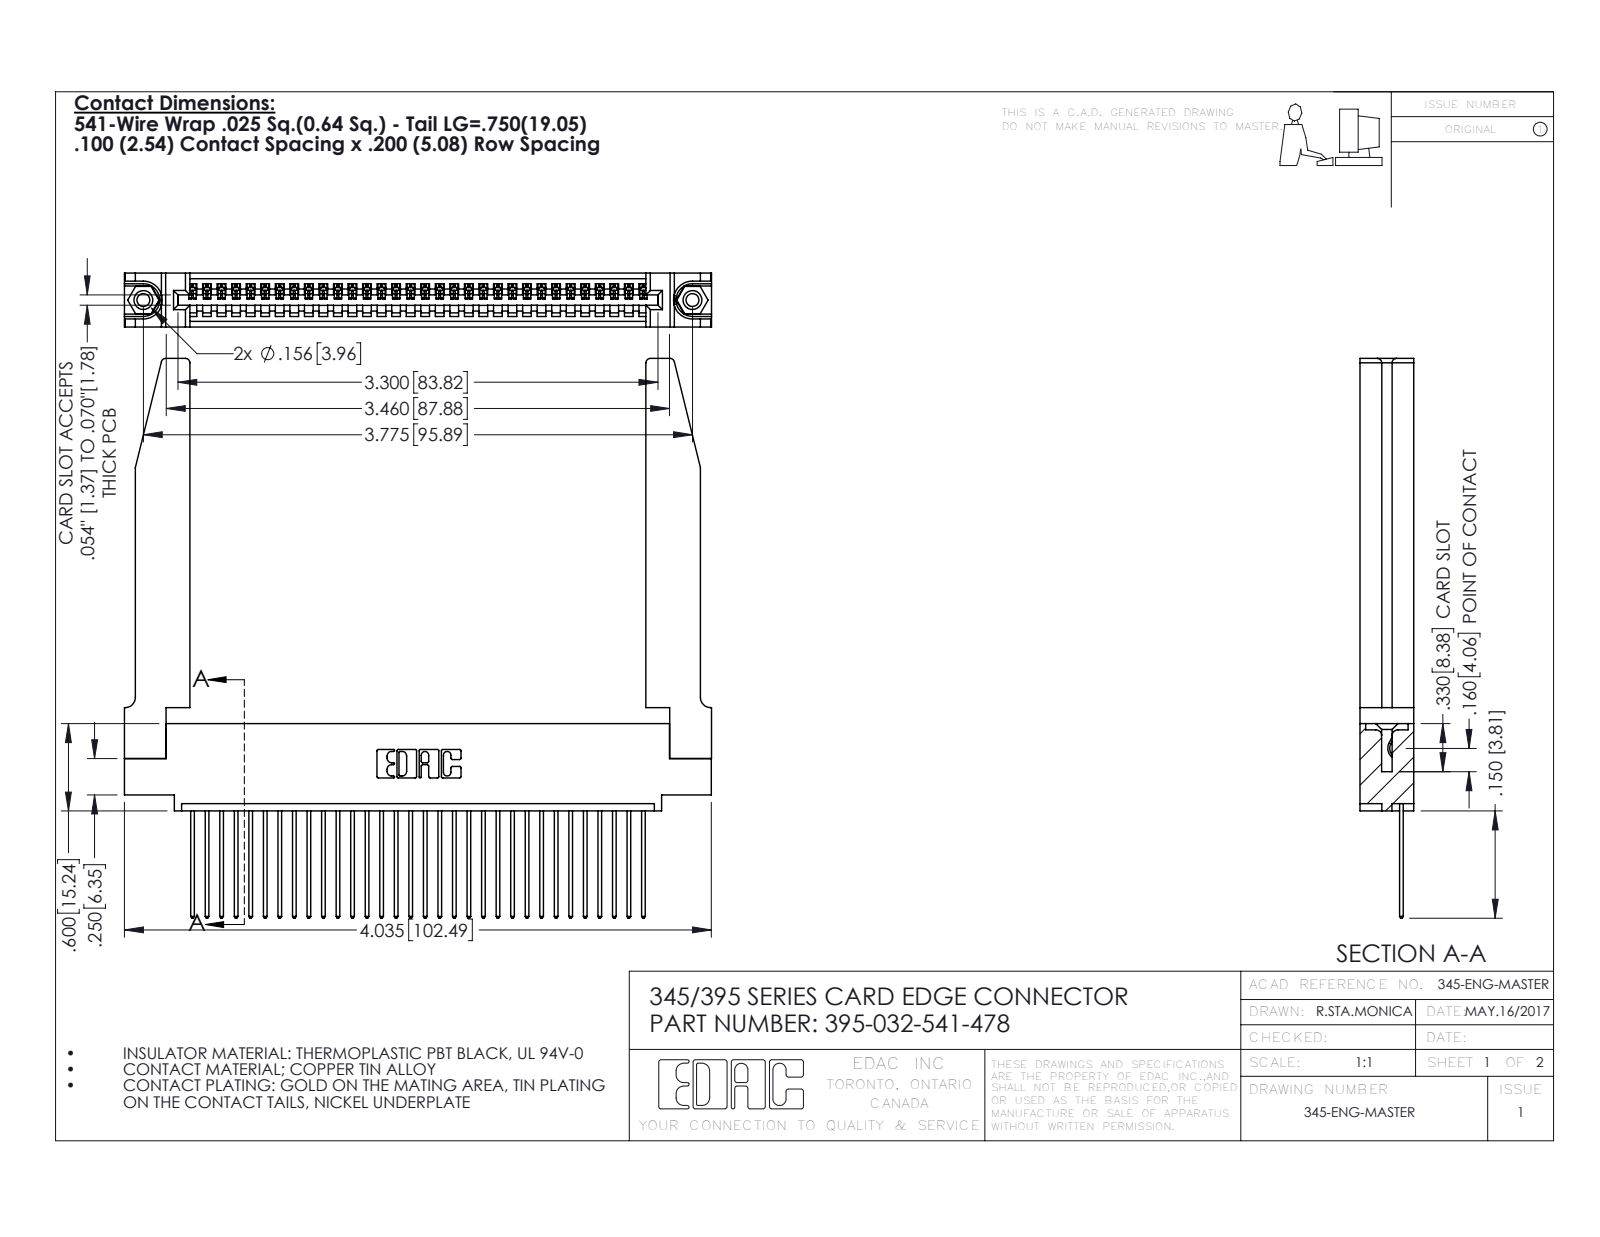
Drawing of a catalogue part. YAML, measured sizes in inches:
part_name: "345 Part_0.110 Offset - 0.156 Dia-TH; 345-220-078_345-220-078; 345-250-001_345-250-001-102; 345-292-001_345-293-141 (+1 more)"
step_written_by: "SolidWorks 2016 (CONFIG_CONTROL_DESIGN)"
units: inches
bodies: {solids: 37, faces: 2220, planar: 1506, cylindrical: 662, other: 52}
overall_size: [4.036, 3.847, 0.37]
volume: 1.065
surface_area: 31.44
round_holes:
  - {diameter: 0.089, count: 2}
  - {diameter: 0.125, count: 2}
  - {diameter: 0.156, count: 2}
  - {diameter: 0.064, count: 1}
round_bosses_or_shafts:
  - {diameter: 0.155, count: 2}
partial_cylinders:
  - {radius: 0.006, count: 64}
  - {radius: 0.01, count: 64}
  - {radius: 0.01, count: 22}
  - {radius: 0.03, count: 8}
  - {radius: 0.007, count: 6}
  - {radius: 0.031, count: 6}
  - {radius: 0.026, count: 3}
  - {radius: 0.031, count: 2}
face_to_face_distances: [0.37, 0.072, 0.298, 0.098, 0.272, 0.025, 0.2, 0.148, 0.15, 0.225]
hole_center_spacings: [0.27, 3.54, 3.775]
